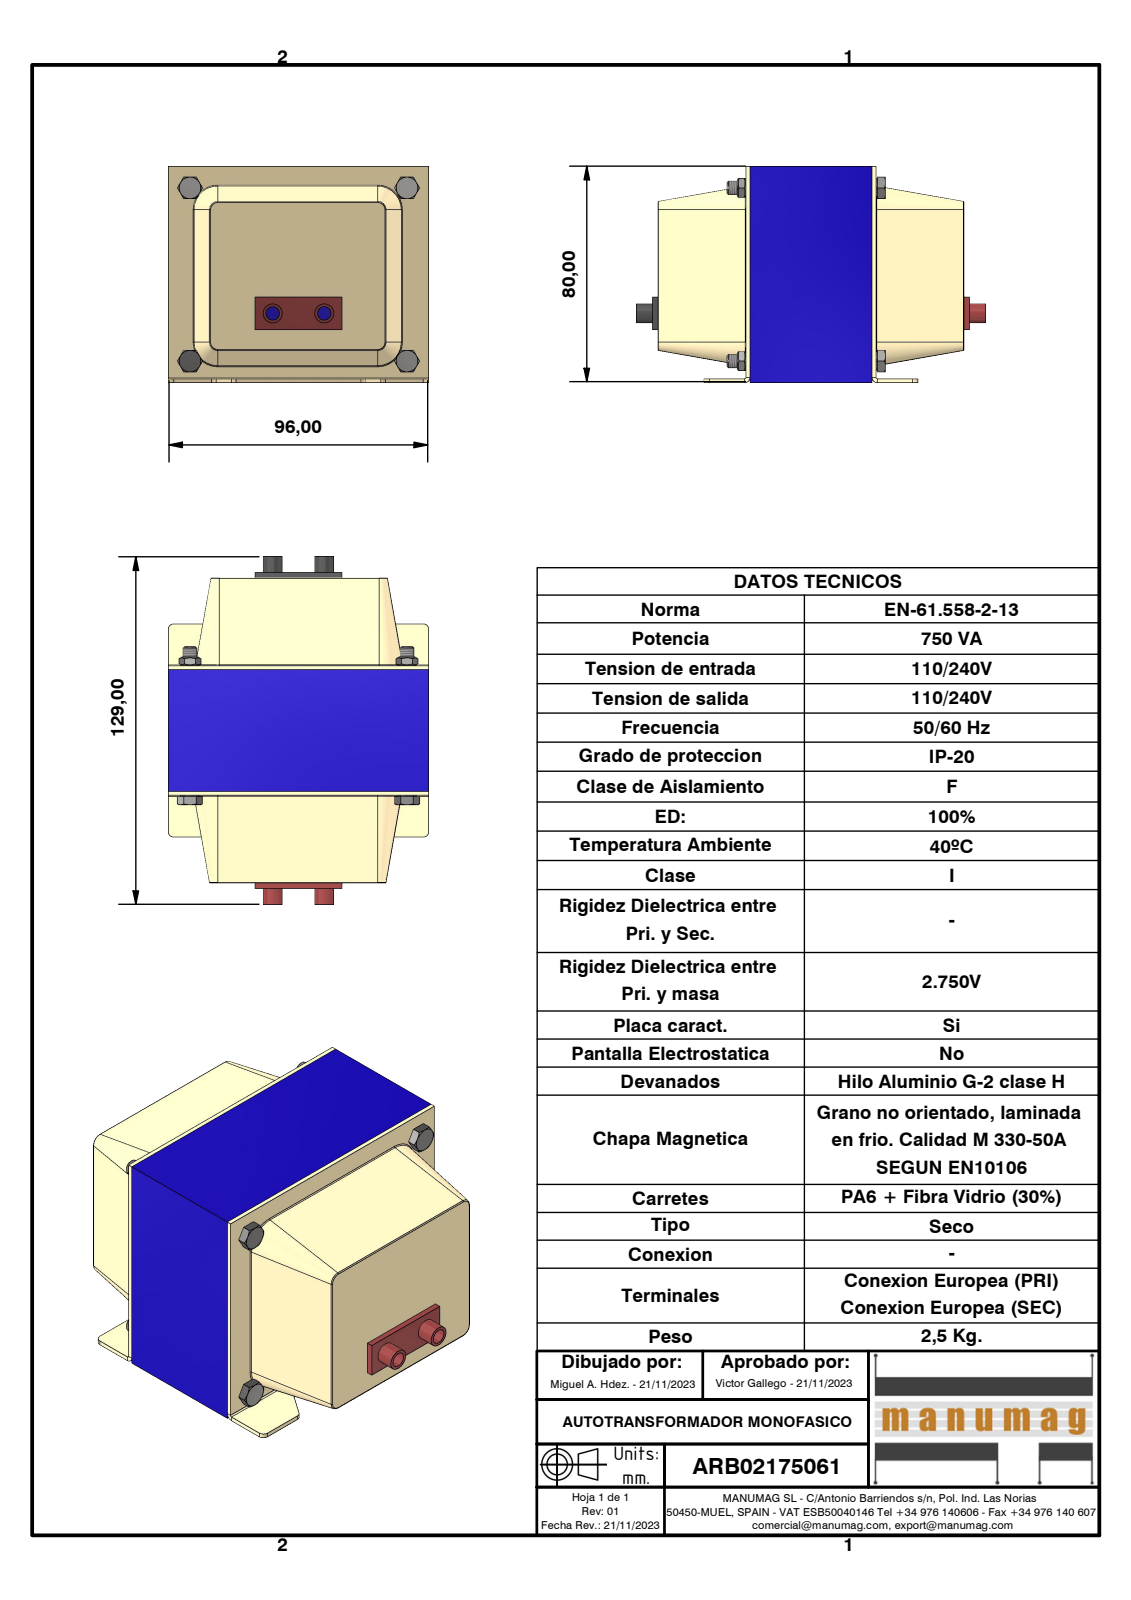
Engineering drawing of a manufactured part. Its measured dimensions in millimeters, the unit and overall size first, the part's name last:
Units: millimetres
Overall size (bounding box): 129 × 96 × 80
Round holes (diameter × count): ⌀5 ×6, ⌀3.24 ×4, ⌀5.5 ×4
Round bosses / shafts (diameter × count): ⌀6.7 ×4, ⌀4.57 ×4, ⌀7 ×2
Partial cylindrical surfaces — rounded edges, fillets, slot ends (radius × count): R0.38 ×16, R2 ×14, R0.5 ×2
Main face-to-face distances: 1.5, 79, 16, 32.5, 64, 80, 45, 48, 32, 34
Hole centre spacings: 35.23, 52.55, 55.5, 64, 67.83, 80, 102.45, 19
Volume: 303 764 mm³ · Surface area: 111 707 mm²
Bodies: 13 solids, 310 faces (162 planar, 68 cylindrical, 80 other)
Part name (STEP PRODUCT): ARB02175061; TAPA RC32 RECEPTACULO; Receptaculo Rojo; Receptaculo negro (+3 more)
STEP written by: Autodesk Inventor 2023 (AUTOMOTIVE_DESIGN)
